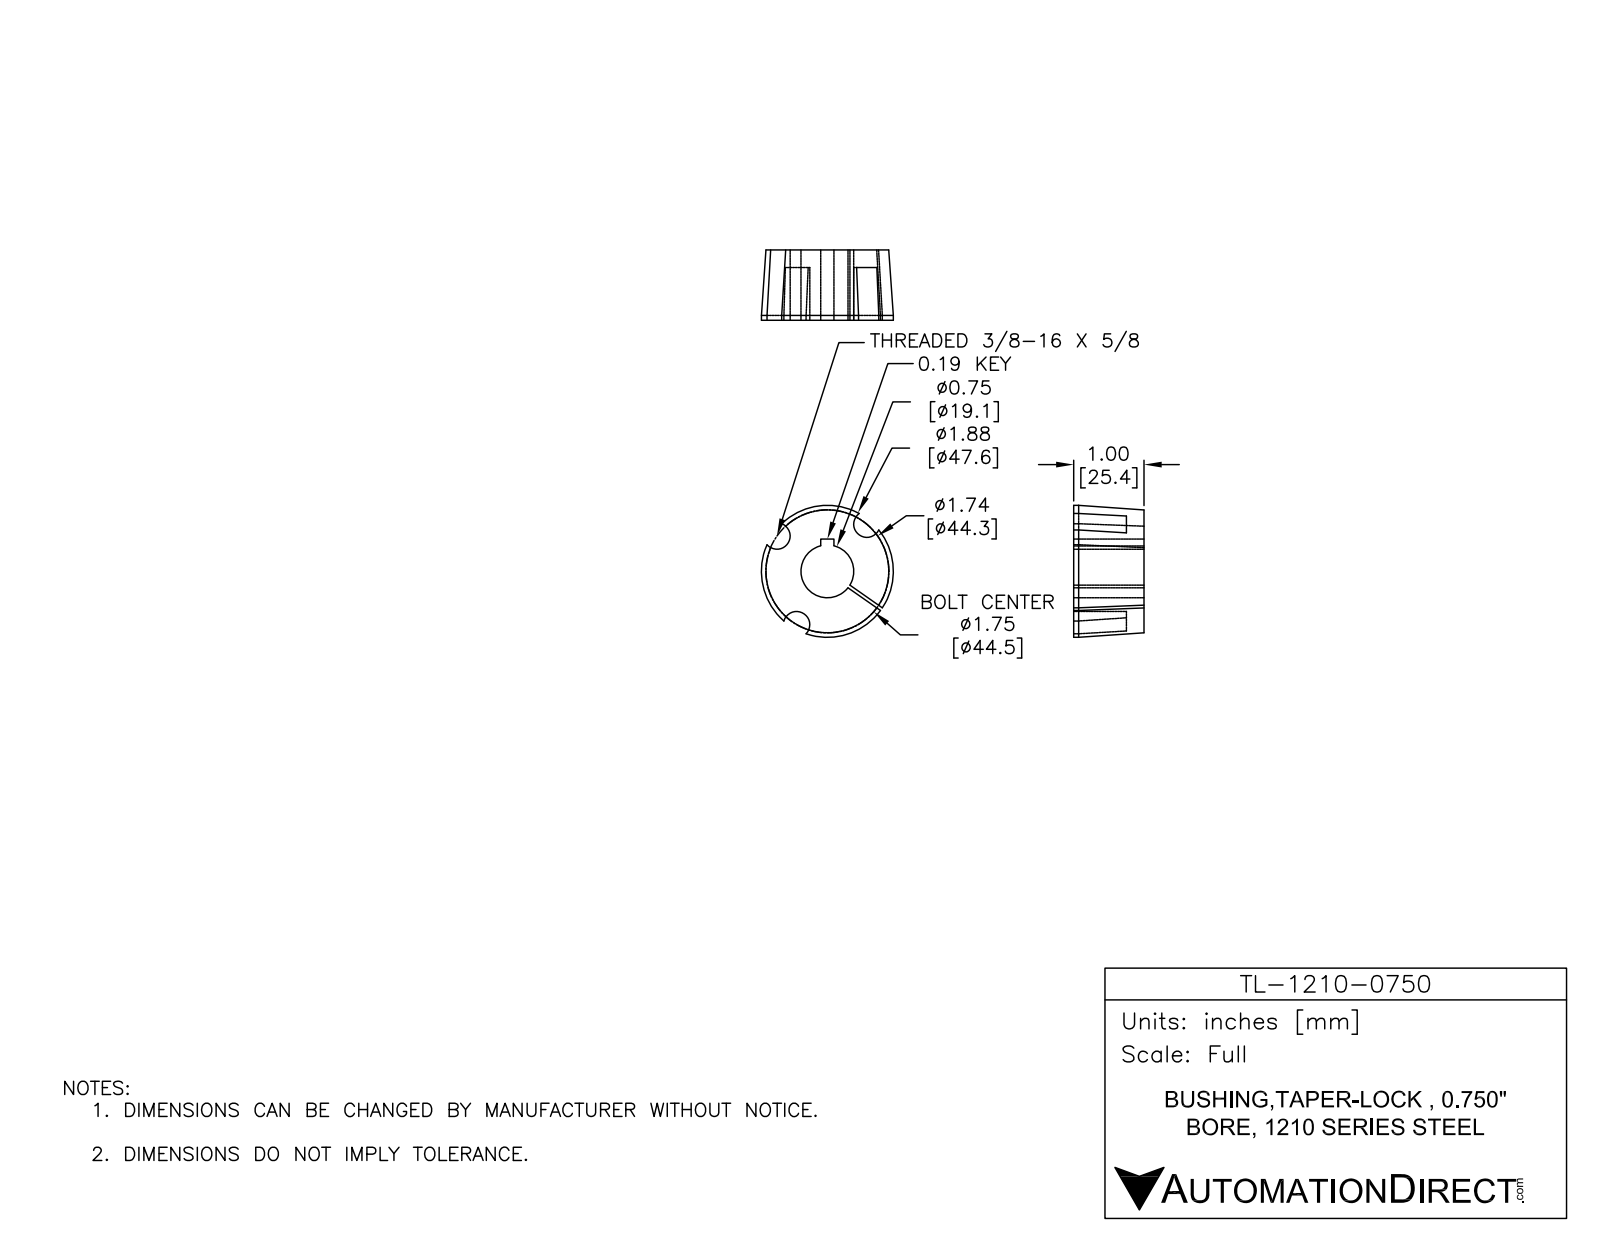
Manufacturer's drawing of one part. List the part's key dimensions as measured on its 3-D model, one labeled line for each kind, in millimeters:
Part name (STEP PRODUCT): TL-1210-0750
STEP written by: SolidWorks 2014 (AUTOMOTIVE_DESIGN)
Units: millimetres
Bodies: 1 solid, 25 faces (9 planar, 13 cylindrical, 3 other)
Overall size (bounding box): 47.6 × 47.6 × 25.4
Volume: 31 760 mm³ · Surface area: 8 948 mm²
Round holes (diameter × count): ⌀19.1 ×1
Round bosses / shafts (diameter × count): ⌀47.6 ×1
Partial cylindrical surfaces — rounded edges, fillets, slot ends (radius × count): R4.8 ×3
Main face-to-face distances: 25.4, 1.2, 6.4, 19.1, 4.7
